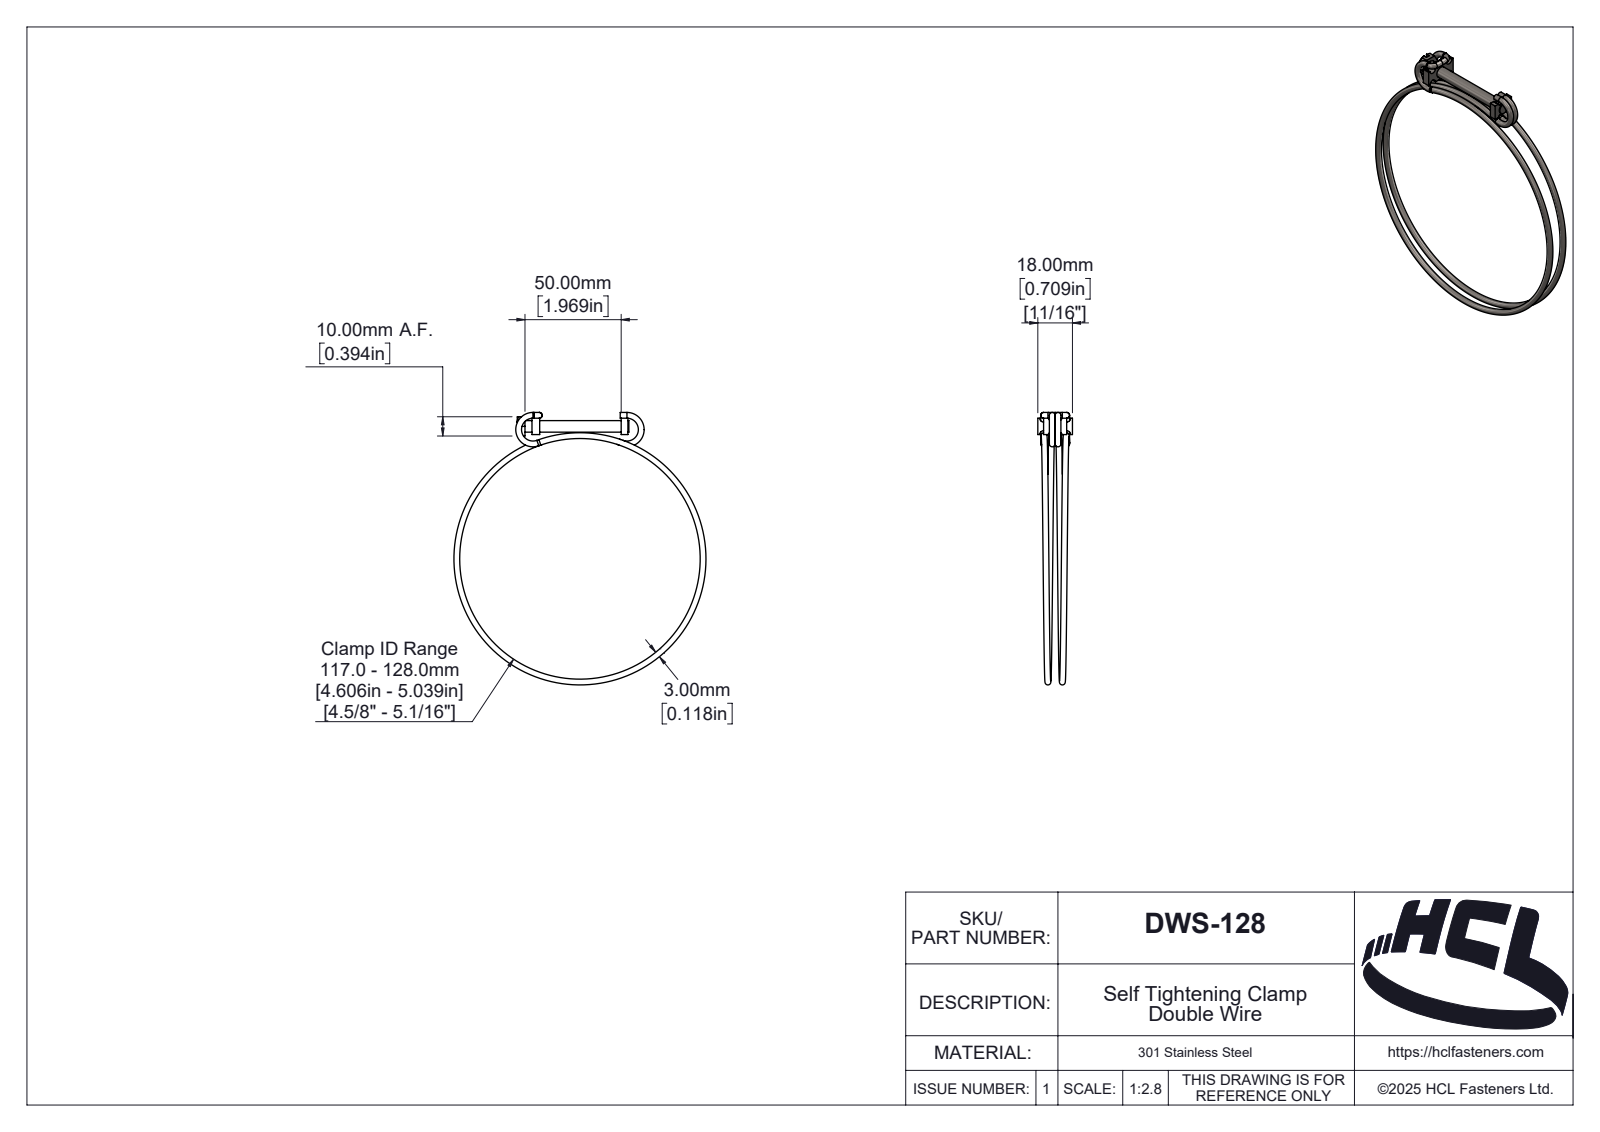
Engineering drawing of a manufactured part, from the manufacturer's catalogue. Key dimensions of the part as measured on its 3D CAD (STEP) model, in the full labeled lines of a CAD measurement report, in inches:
Part name (STEP PRODUCT): DWS-128
STEP written by: SolidWorks 2025 (AUTOMOTIVE_DESIGN)
Units: inches
Bodies: 6 solids, 213 faces (55 planar, 74 cylindrical, 84 other)
Overall size (bounding box): 5.573 × 5.157 × 0.709
Volume: 0.589 in³ · Surface area: 18.4 in²
Round holes (diameter × count): ⌀0.236 ×1
Round bosses / shafts (diameter × count): ⌀0.118 ×4
Partial cylindrical surfaces — rounded edges, fillets, slot ends (radius × count): R0.008 ×12, R0.039 ×4, R0.079 ×4, R0.016 ×1, R0.02 ×1, R0.021 ×1, R0.025 ×1, R0.036 ×1
Main face-to-face distances: 0.157, 0.301, 0.394, 1.825, 0.118, 2.126, 1.806, 2.106, 0.039, 1.668
